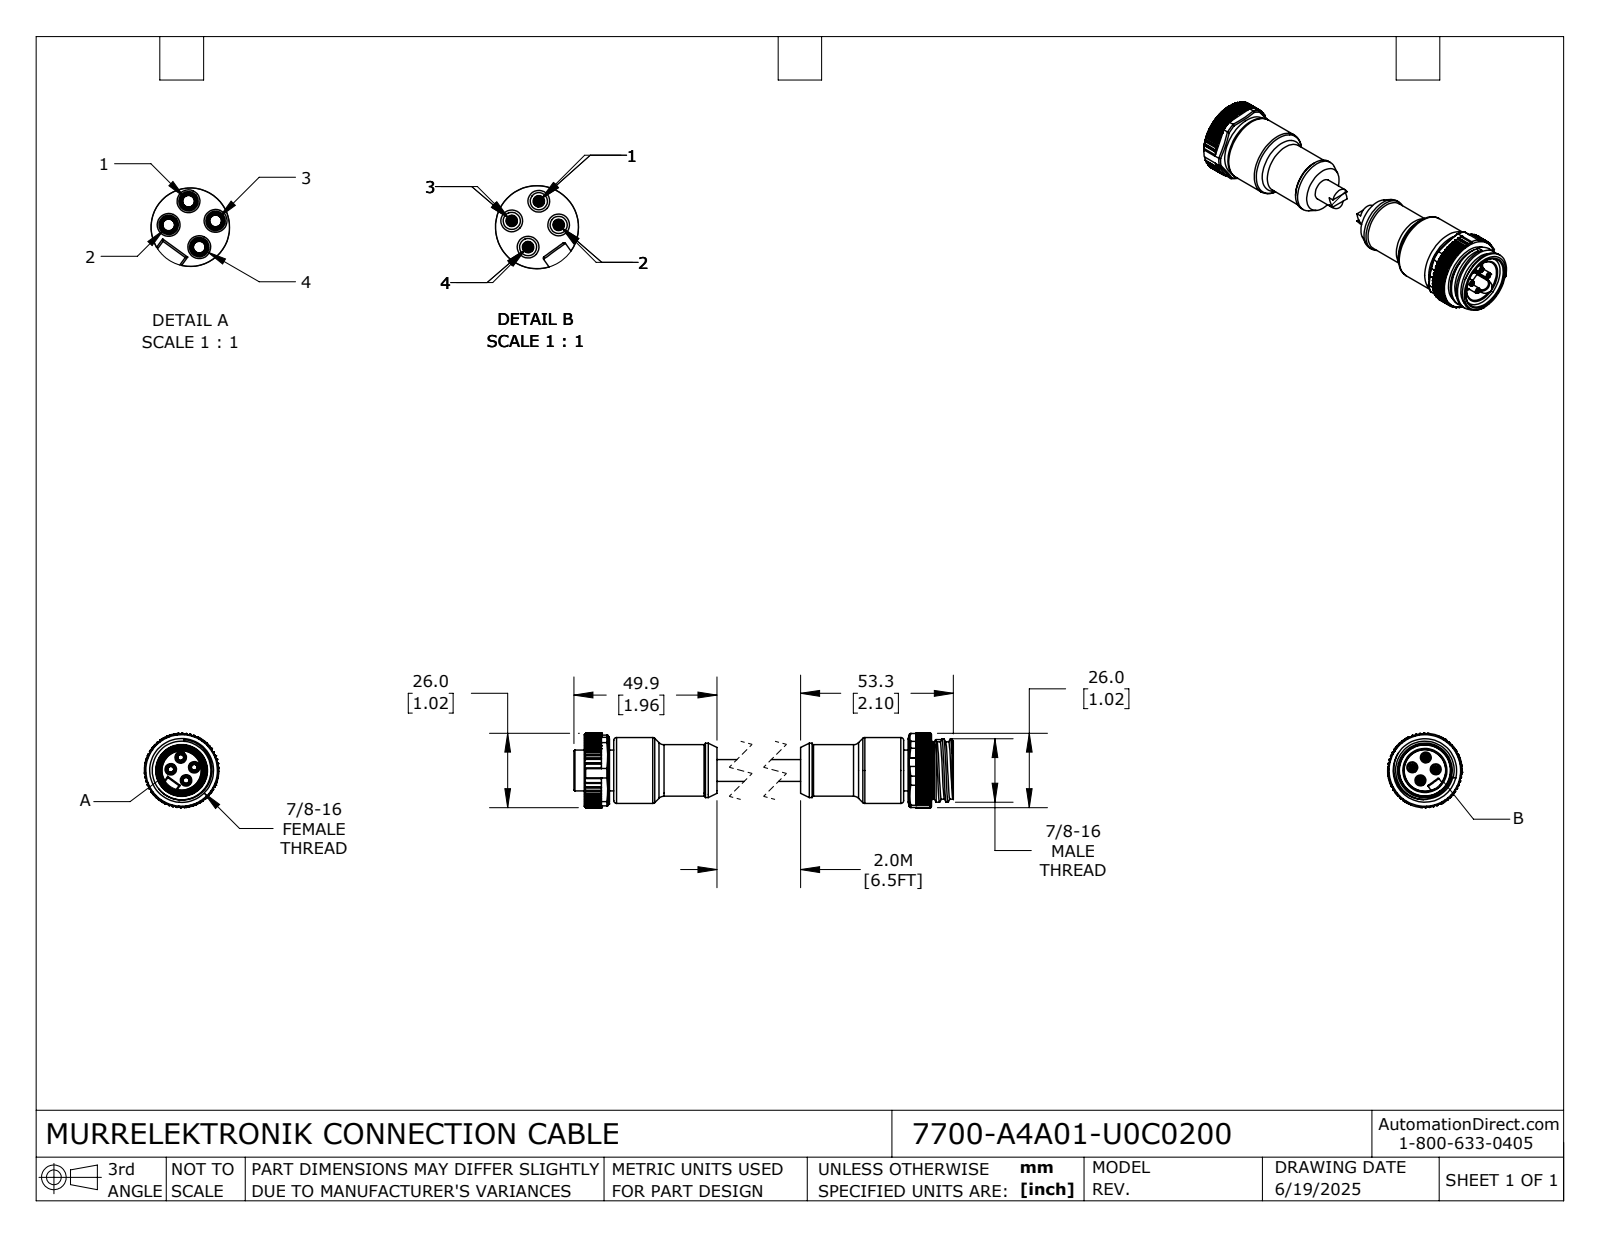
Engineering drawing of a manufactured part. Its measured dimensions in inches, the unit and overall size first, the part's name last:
Units: inches
Overall size (bounding box): 5.244 × 1.024 × 1.024
Round holes (diameter × count): ⌀0.081 ×4, ⌀0.118 ×4, ⌀0.134 ×4, ⌀0.61 ×1, ⌀0.614 ×1, ⌀0.728 ×1, ⌀0.807 ×1, ⌀0.875 ×1
Round bosses / shafts (diameter × count): ⌀0.079 ×4, ⌀0.906 ×1, ⌀0.873 ×1, ⌀0.789 ×1, ⌀0.787 ×1, ⌀0.748 ×1, ⌀0.713 ×1, ⌀0.709 ×1
Partial cylindrical surfaces — rounded edges, fillets, slot ends (radius × count): R0.008 ×252, R0.012 ×18, R0.004 ×8, R0.027 ×4, R0.029 ×4, R0.093 ×1, R0.512 ×1
Main face-to-face distances: 0.059, 4.075, 1.476, 2.657, 1.417, 2.598, 4.134, 0.346, 4.421, 0.287
Hole centre spacings: 0.15, 0.324, 0.179, 0.179, 0.212, 0.213, 0.23, 0.26
Volume: 2.059 in³ · Surface area: 22.09 in²
Bodies: 2 solids, 1226 faces (520 planar, 543 cylindrical, 163 other)
Part name (STEP PRODUCT): 7700-A4A01-U0C0200_FEMALE; 7700-A4A01-U0C0200_MALE; 7700-A4A01-U0C0200
STEP written by: SolidWorks 2024 (CONFIG_CONTROL_DESIGN)
